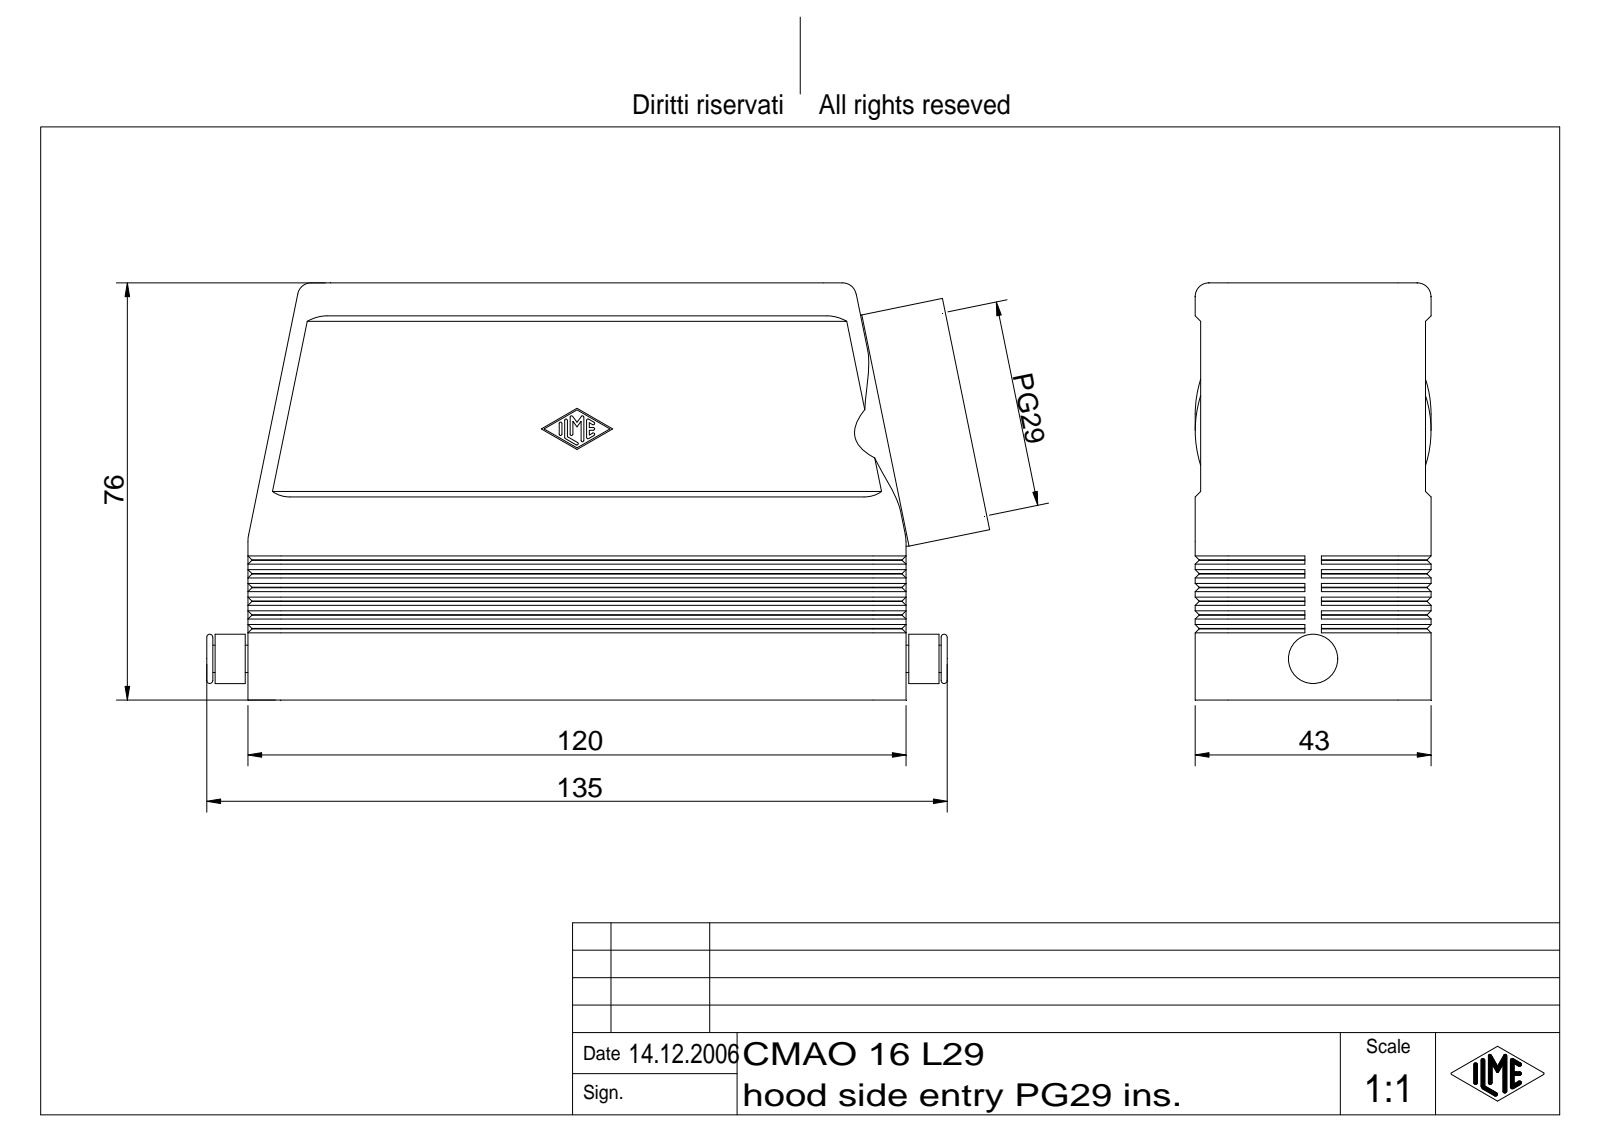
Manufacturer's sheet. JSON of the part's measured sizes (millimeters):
{"part_name": "CH Tüllengehäuse für einen Einsatz Teil 5", "step_written_by": "Autodesk Inventor 7 (AUTOMOTIVE_DESIGN)", "units": "millimeters", "bodies": {"solids": 1, "faces": 534, "planar": 194, "cylindrical": 136, "other": 204}, "overall_size": [142.74, 76, 43], "volume_mm3": 88281, "surface_area_mm2": 57908, "round_holes": [[33.48, 1], [35.48, 1]], "round_bosses_or_shafts": [[43, 1], [9, 1], [5, 1]], "partial_cylinders_radius": [[0.25, 14], [6, 10], [2, 4], [2.5, 4], [3, 4], [5.3, 2]], "face_to_face_distances": [3, 37, 40, 1, 2, 42, 39, 43, 41, 1.77]}
